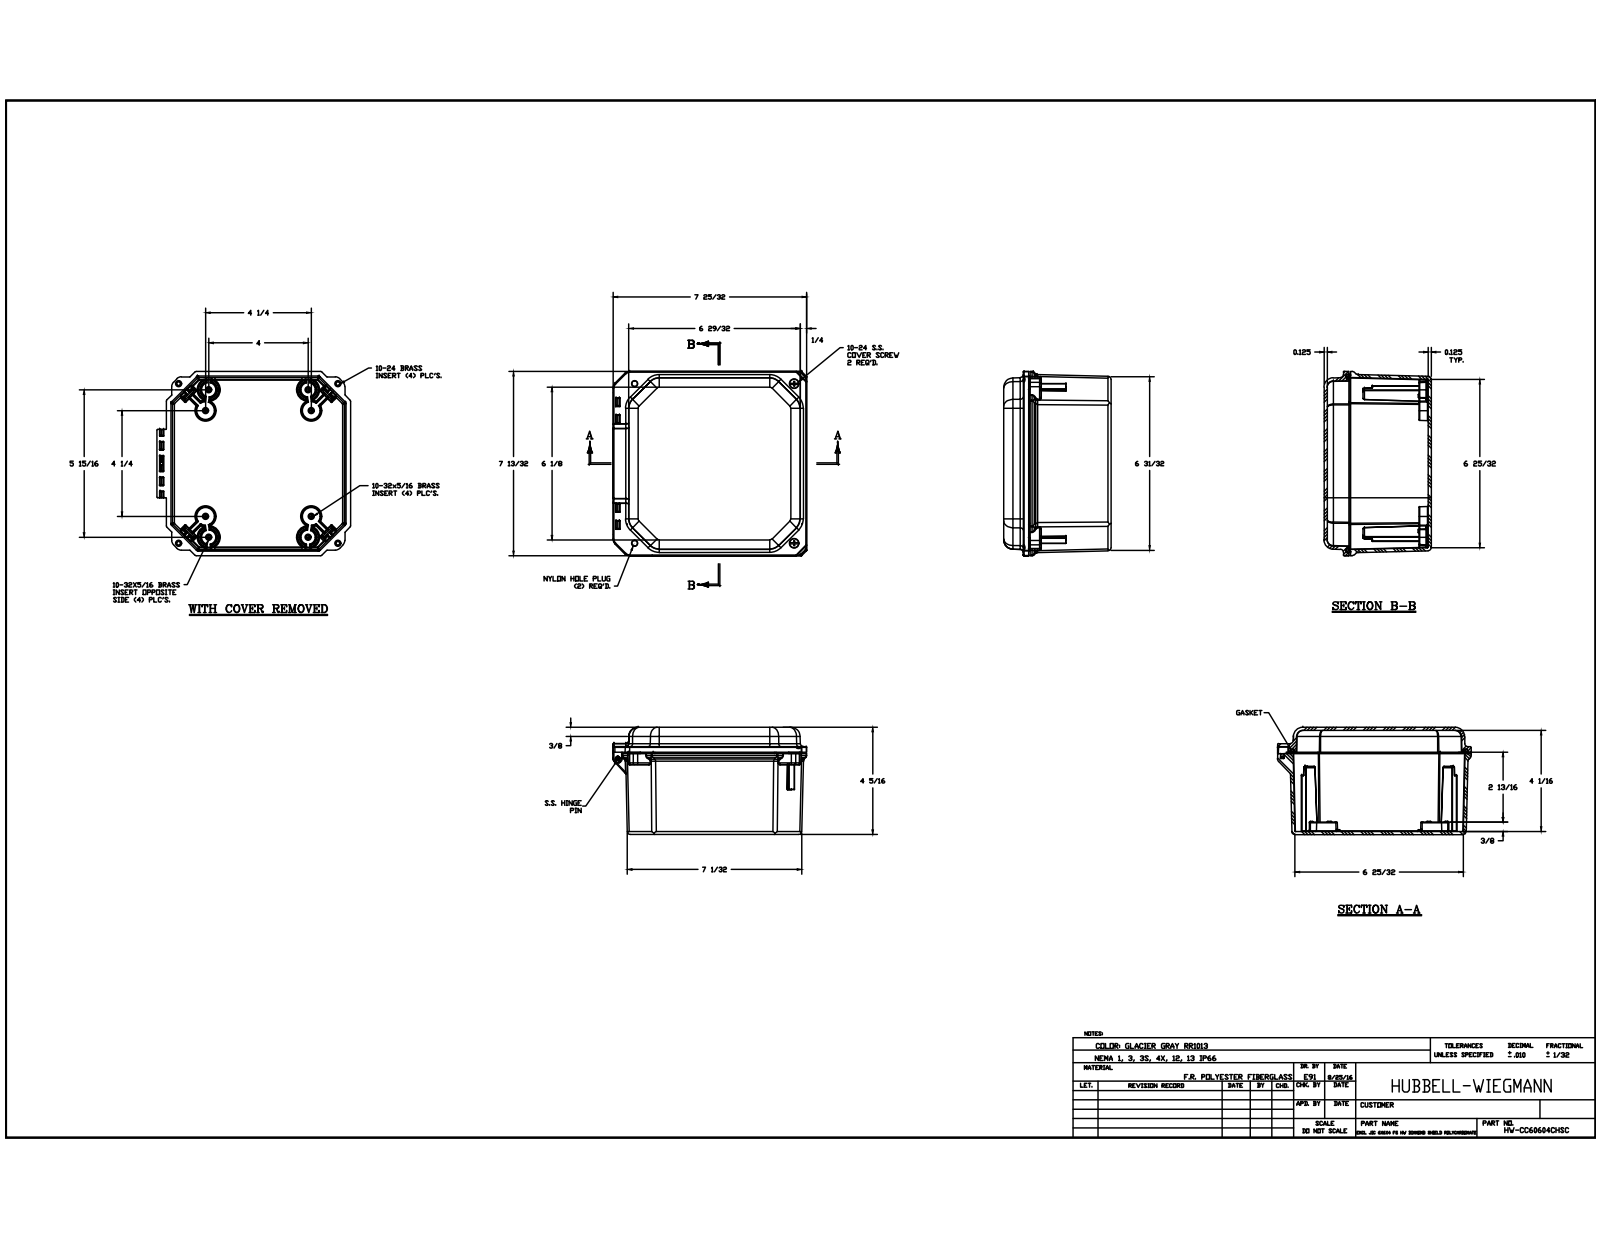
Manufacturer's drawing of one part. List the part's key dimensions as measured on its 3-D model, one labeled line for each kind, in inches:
Part name (STEP PRODUCT): HW-CC60604CHSC; DS060604BOX; BRASS INSERT-(; BRASS INSERT-(_1 (+7 more)
STEP written by: Autodesk Inventor 2017 (CONFIG_CONTROL_DESIGN)
Units: inches
Bodies: 25 solids, 1943 faces (538 planar, 709 cylindrical, 696 other)
Overall size (bounding box): 7.791 × 7.416 × 4.312
Volume: 31.75 in³ · Surface area: 480.6 in²
Round holes (diameter × count): ⌀0.156 ×12, ⌀0.152 ×8, ⌀0.219 ×4, ⌀0.252 ×4, ⌀0.312 ×4, ⌀0.15 ×2, ⌀0.137 ×1
Round bosses / shafts (diameter × count): ⌀0.246 ×12, ⌀0.87 ×4, ⌀0.45 ×2, ⌀0.209 ×2, ⌀0.199 ×2, ⌀0.135 ×1
Partial cylindrical surfaces — rounded edges, fillets, slot ends (radius × count): R0.01 ×136, R0.005 ×96, R0.02 ×65, R0.03 ×38, R0.125 ×29, R0.03 ×24, R0.09 ×24, R0.25 ×24
Main face-to-face distances: 0.125, 4.187, 4.312, 4.062, 0.124, 0.125, 3.531, 0.656, 0.375, 1
Hole centre spacings: 5.441, 7.541, 1.53, 5.441, 4.25, 6.01, 6.552, 5.091
